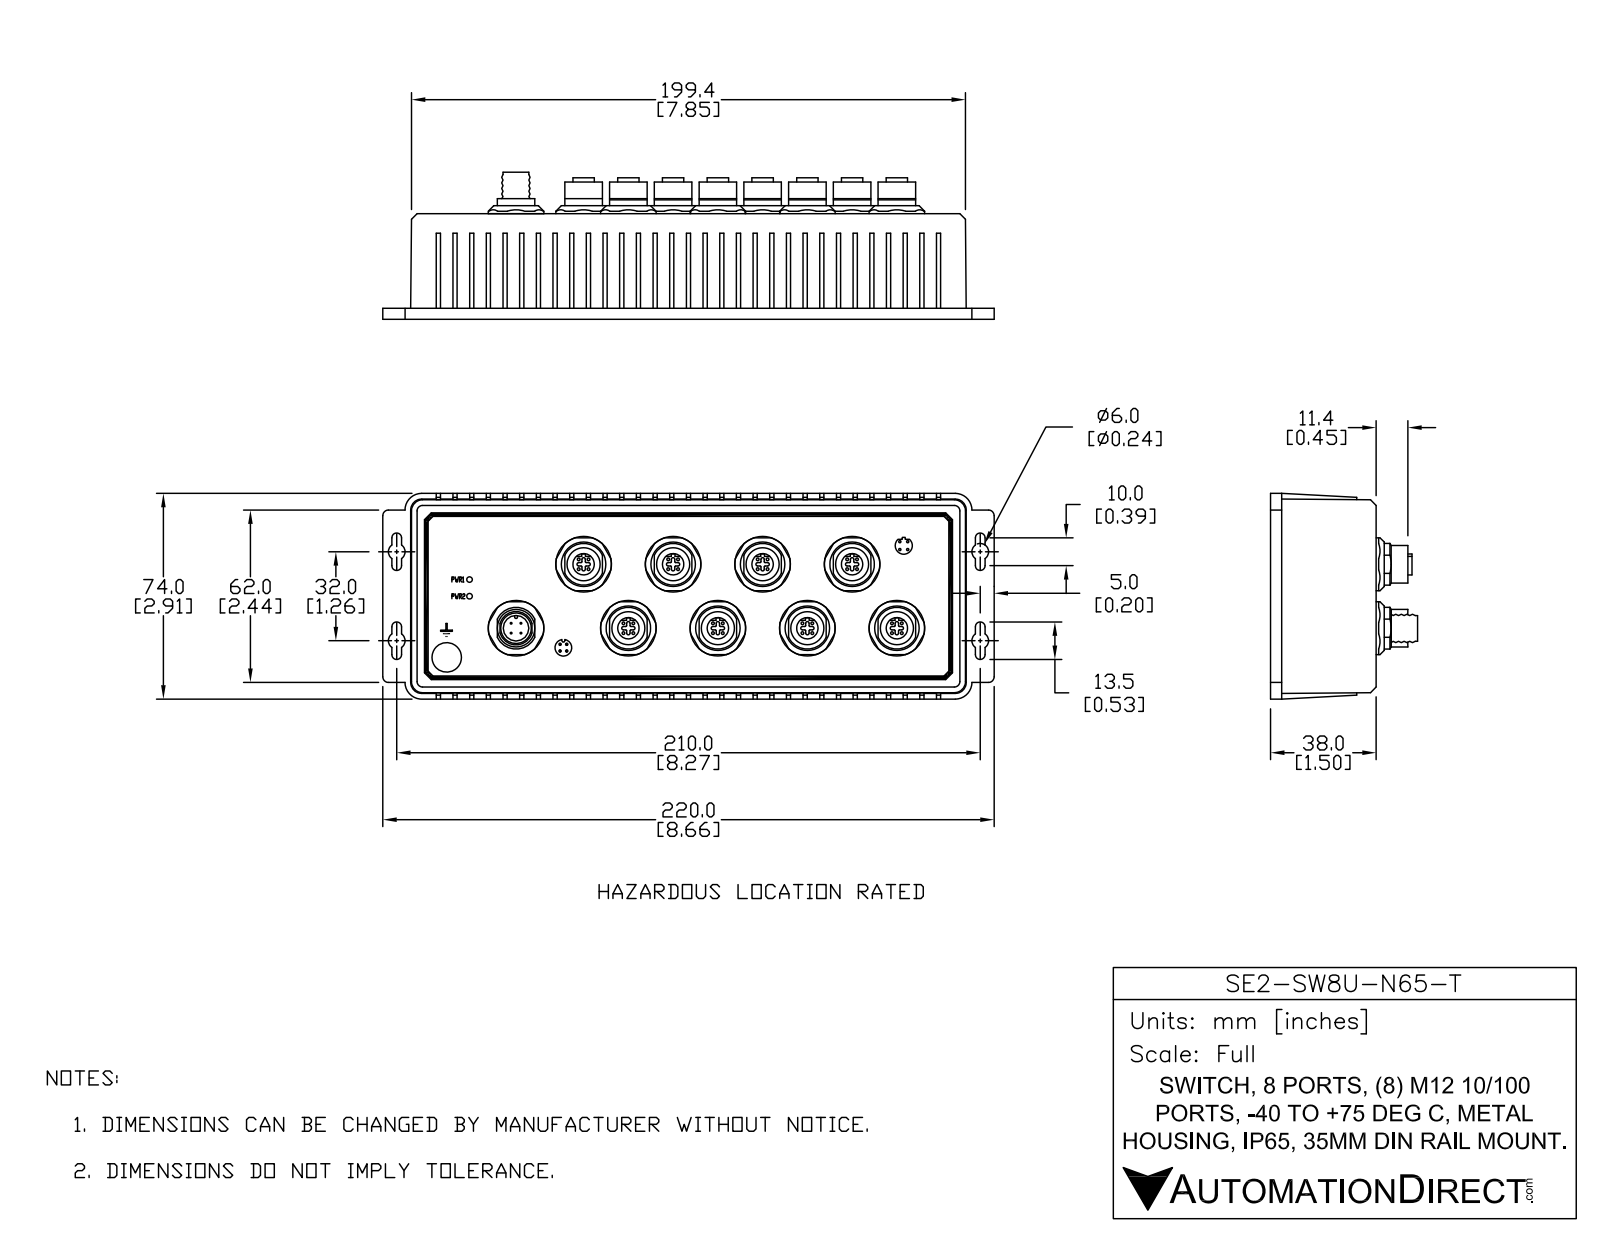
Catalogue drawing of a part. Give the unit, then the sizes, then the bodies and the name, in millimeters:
Units: millimetres
Overall size (bounding box): 222.4 × 78.4 × 51.8
Round holes (diameter × count): ⌀1 ×32, ⌀3 ×18, ⌀14.7 ×9, ⌀11.1 ×8, ⌀17.5 ×8, ⌀3.8 ×1, ⌀5 ×1, ⌀9.5 ×1, ⌀21 ×1
Round bosses / shafts (diameter × count): ⌀12.7 ×9, ⌀22.7 ×8, ⌀15.9 ×7, ⌀0.8 ×4, ⌀15.9 ×2, ⌀8 ×1, ⌀3.5 ×1
Partial cylindrical surfaces — rounded edges, fillets, slot ends (radius × count): R0.3 ×80, R3 ×34, R2 ×32, R0.5 ×28, R1.8 ×8, R2.7 ×8, R3.3 ×8, R3.8 ×8
Main face-to-face distances: 1.5, 3.5, 0.5, 35.3, 32.3, 3, 33.8, 36.8, 1, 35.8
Hole centre spacings: 28.1, 32.2, 53.5, 64.4, 13.2, 13.2, 18.9, 39.6
Volume: 179 400 mm³ · Surface area: 135 200 mm²
Bodies: 22 solids, 1409 faces (790 planar, 398 cylindrical, 221 other)
Part name (STEP PRODUCT): SE2-SW5U-N65-T
STEP written by: SolidWorks 2017 (AUTOMOTIVE_DESIGN)
